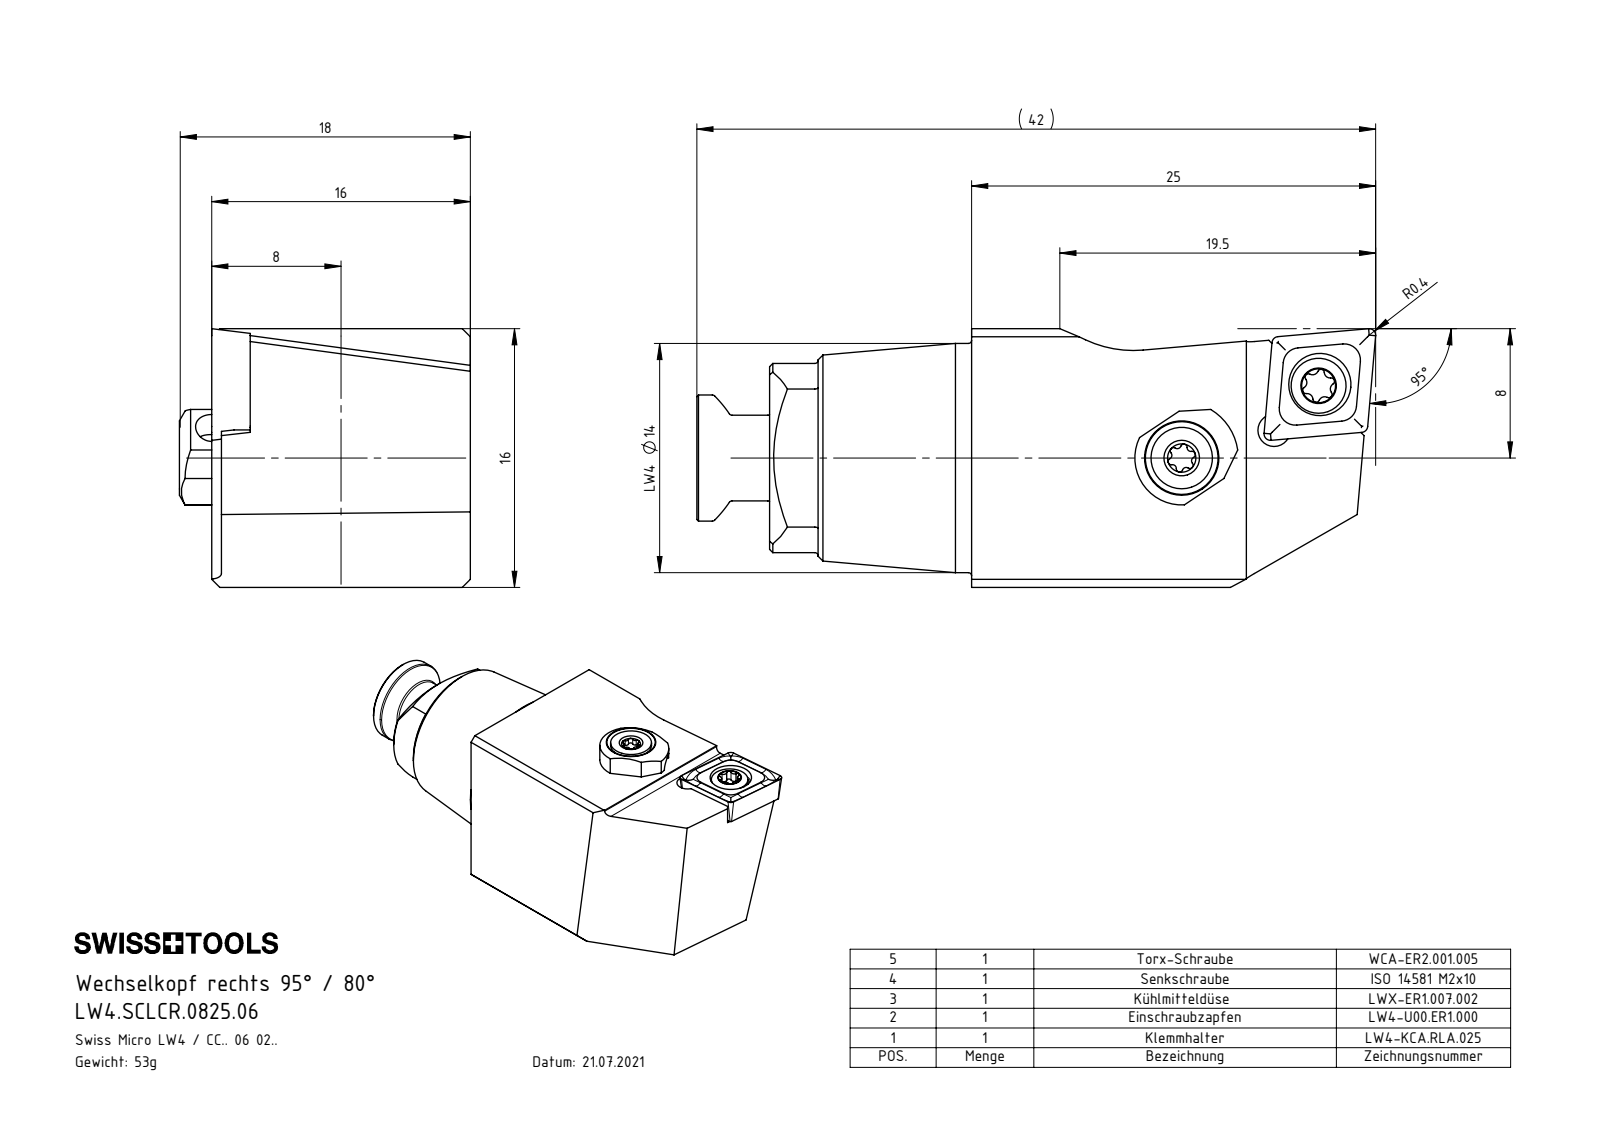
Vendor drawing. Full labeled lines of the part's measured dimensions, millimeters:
Part name (STEP PRODUCT): LW4-KCA.RLA.025_A; LW4-U00.ER1.000_B; CCMT060204; LW4.SCLCR.0825.06 (+3 more)
STEP written by: SolidWorks 2022 (CONFIG_CONTROL_DESIGN)
Units: millimetres
Bodies: 6 solids, 259 faces (69 planar, 83 cylindrical, 107 other)
Overall size (bounding box): 42 × 19.5 × 16
Volume: 6 747 mm³ · Surface area: 3 625 mm²
Round holes (diameter × count): ⌀2 ×3, ⌀3 ×2, ⌀1.6 ×1, ⌀2.05 ×1, ⌀2.5 ×1, ⌀2.8 ×1, ⌀3.85 ×1, ⌀5.5 ×1
Round bosses / shafts (diameter × count): ⌀14.17 ×1, ⌀7.7 ×1, ⌀6 ×1, ⌀5.3 ×1, ⌀5 ×1, ⌀3.8 ×1, ⌀3.4 ×1, ⌀2.5 ×1
Partial cylindrical surfaces — rounded edges, fillets, slot ends (radius × count): R0.2 ×8, R0.21 ×6, R0.24 ×6, R0.36 ×5, R0.36 ×1, R0.5 ×1, R2.9 ×1, R4.5 ×1
Main face-to-face distances: 16, 7.5, 13.62, 2.38, 15.4, 1.78, 0.6, 12.5, 2, 4
Hole centre spacings: 3.9, 4.02, 5.96, 9.58, 9.69
